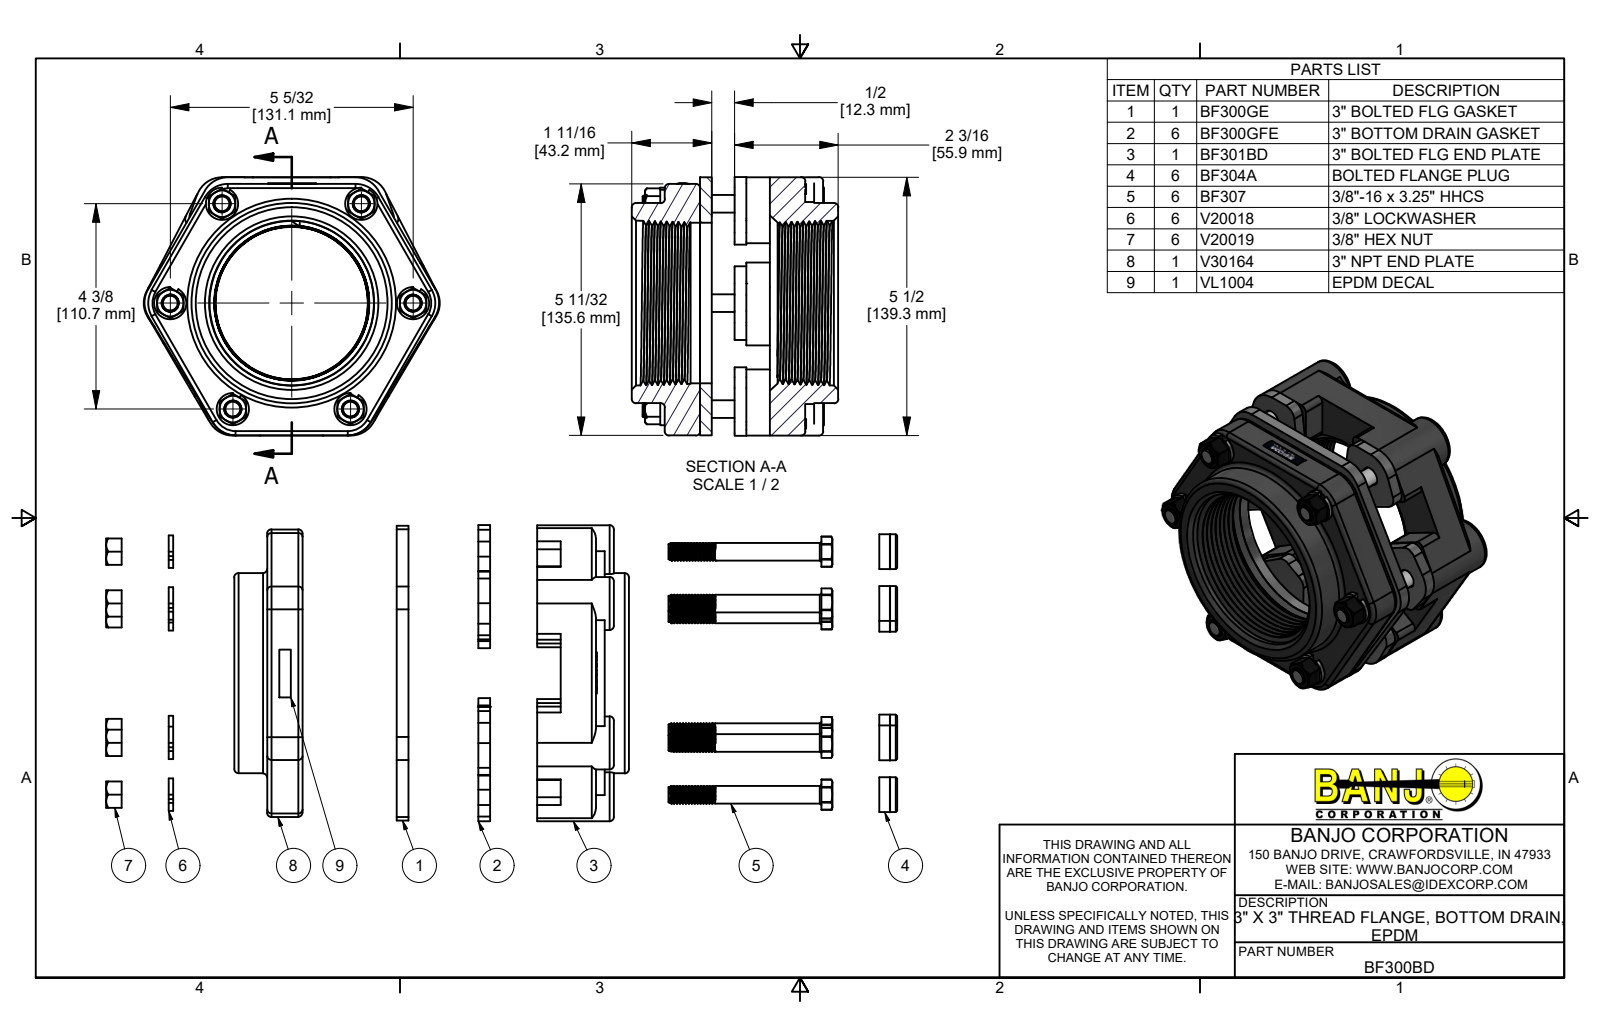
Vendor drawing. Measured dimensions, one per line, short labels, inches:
name: BF300BD; BF301BD; BF300GE; V30164 (+6 more)
written by: Autodesk Inventor 2019 (AUTOMOTIVE_DESIGN)
unit: in
bodies: 34 solids, 1611 faces (511 planar, 528 cylindrical, 572 other)
size: 6.293 × 5.492 × 4.386
volume: 47.06 in³; area: 321.8 in²
holes: 6× ⌀0.307, 6× ⌀0.385, 6× ⌀0.406, 6× ⌀0.406, 6× ⌀0.41, 6× ⌀0.715, 6× ⌀0.75, 1× ⌀3.41
bosses: 90× ⌀0.324, 6× ⌀1.125, 6× ⌀0.742, 6× ⌀0.687, 6× ⌀0.375, 1× ⌀4.25
rounds: 24× R0.125, 24× R0.25, 18× R0.09, 12× R0.162, 12× R0.56, 6× R0.32, 6× R0.562, 3× R1.71
face distances: 0.25, 0.736, 0.75, 0.986, 1.486, 2.236, 0.486, 1, 1.736, 1.236
hole spacings: 2.38, 2.574, 2.577, 2.58, 2.614, 4.366, 4.442, 4.575
